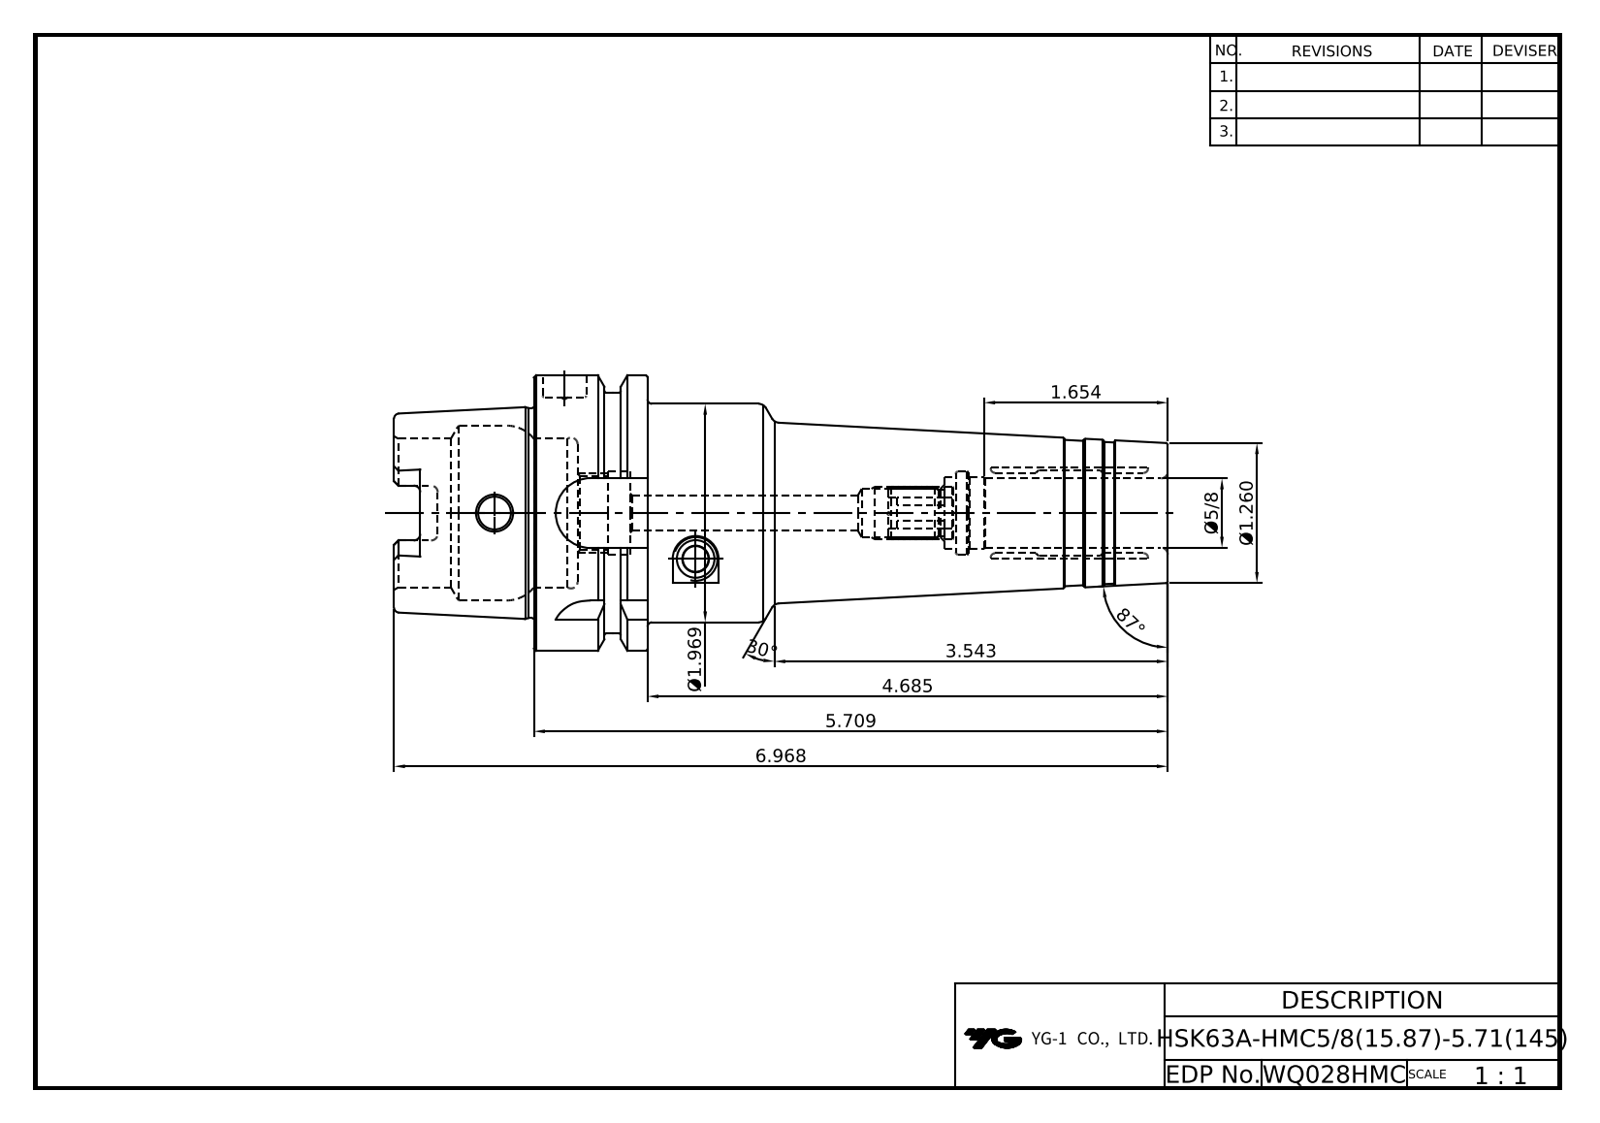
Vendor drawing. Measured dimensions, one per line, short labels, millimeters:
name: LO-HSK63A-HMC15.875-145
written by: Autodesk Inventor 2020 (AUTOMOTIVE_DESIGN)
unit: mm
bodies: 1 solid, 135 faces (42 planar, 34 cylindrical, 59 other)
size: 177 × 63 × 63
volume: 218 701 mm³; area: 40 791 mm²
holes: 1× ⌀7.5, 1× ⌀8, 1× ⌀10, 1× ⌀10.92, 1× ⌀15.88, 1× ⌀16.4, 1× ⌀16.92, 1× ⌀19, 1× ⌀34, 1× ⌀40
bosses: 1× ⌀63, 1× ⌀55, 1× ⌀50, 1× ⌀48.04
rounds: 6× R1.5, 4× R2.88, 4× R8
face distances: 26, 10, 16, 145, 119, 135, 32, 42, 58, 177
